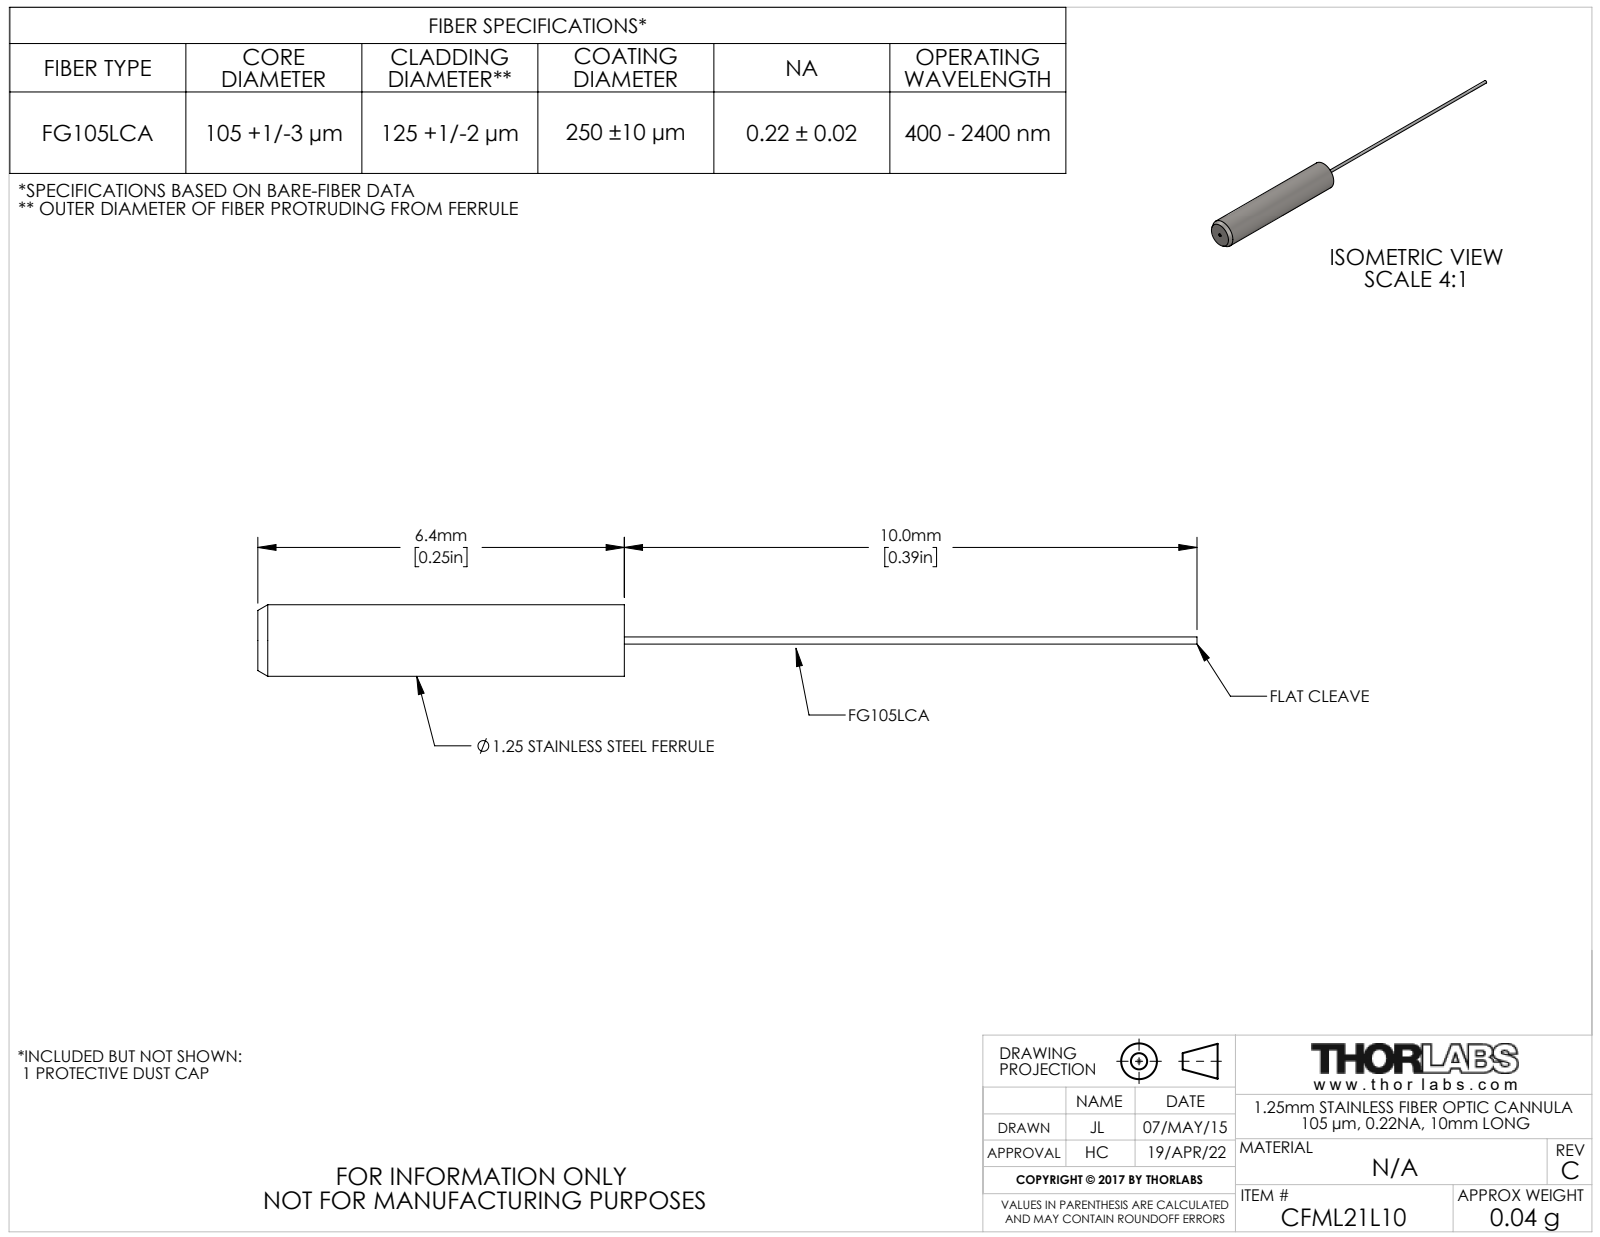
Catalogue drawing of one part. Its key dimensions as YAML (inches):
part_name: "TTN041713-E0W"
step_written_by: "SolidWorks 2014 (CONFIG_CONTROL_DESIGN)"
units: inches
bodies: {solids: 2, faces: 18, planar: 4, cylindrical: 8, other: 6}
overall_size: [0.646, 0.049, 0.049]
round_holes:
  - {diameter: 0.039, count: 1}
round_bosses_or_shafts:
  - {diameter: 0.049, count: 1}
face_to_face_distances: [0.252, 0.646, 0.394]
